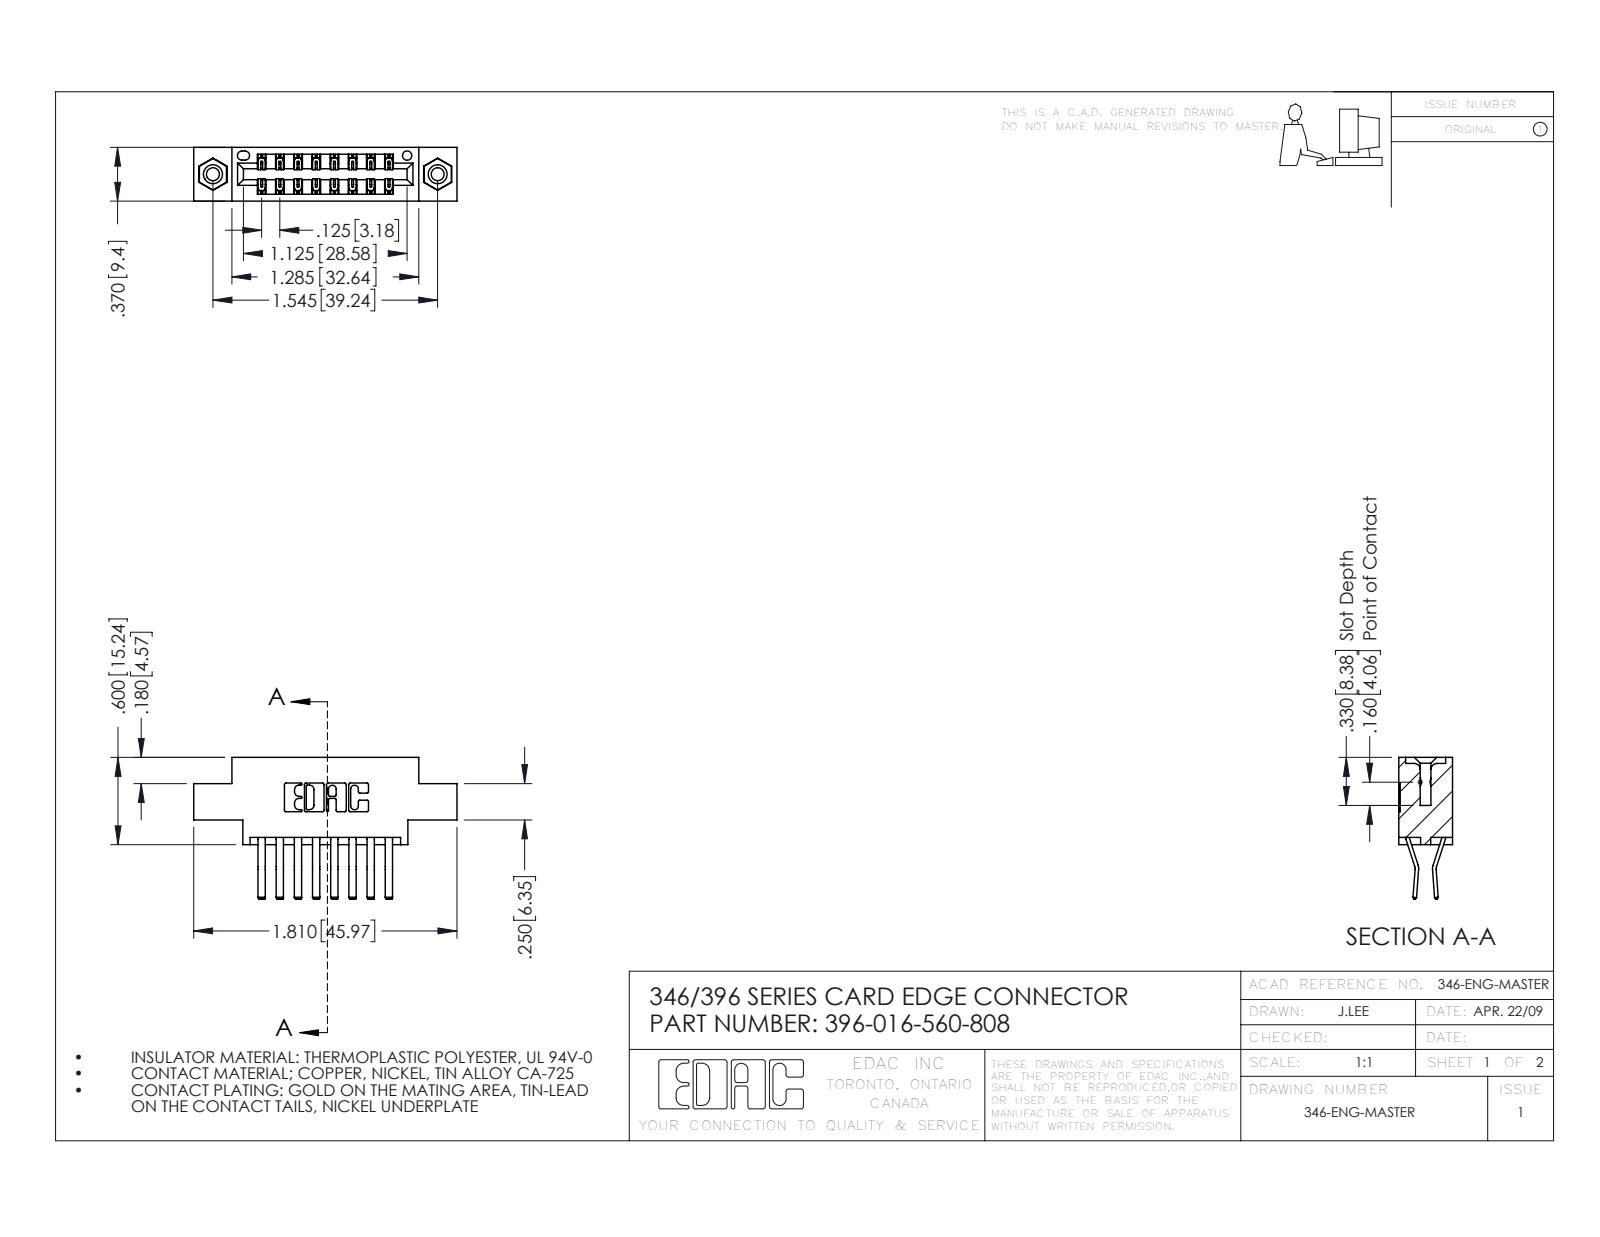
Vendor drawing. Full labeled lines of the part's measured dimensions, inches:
Part name (STEP PRODUCT): 345-250-001_345-250-003-102; 396-016-560-808; 345-292-001_560 Tail; 346 Part_0.170 Offset - 0.156 Dia-TI
STEP written by: SolidWorks 2016 (CONFIG_CONTROL_DESIGN)
Units: inches
Bodies: 19 solids, 1050 faces (672 planar, 362 cylindrical, 16 other)
Overall size (bounding box): 1.81 × 0.975 × 0.37
Volume: 0.254 in³ · Surface area: 8.784 in²
Round holes (diameter × count): ⌀0.089 ×2, ⌀0.125 ×2, ⌀0.156 ×2, ⌀0.064 ×1
Round bosses / shafts (diameter × count): ⌀0.155 ×2
Partial cylindrical surfaces — rounded edges, fillets, slot ends (radius × count): R0.006 ×24, R0.01 ×22, R0.007 ×6, R0.031 ×6, R0.026 ×3, R0.01 ×2, R0.014 ×2, R0.022 ×2
Main face-to-face distances: 0.25, 0.37, 0.048, 0.322, 0.025, 0.222, 0.148, 0.1, 0.174, 0.072
Hole centre spacings: 0.246, 1.341, 1.545
